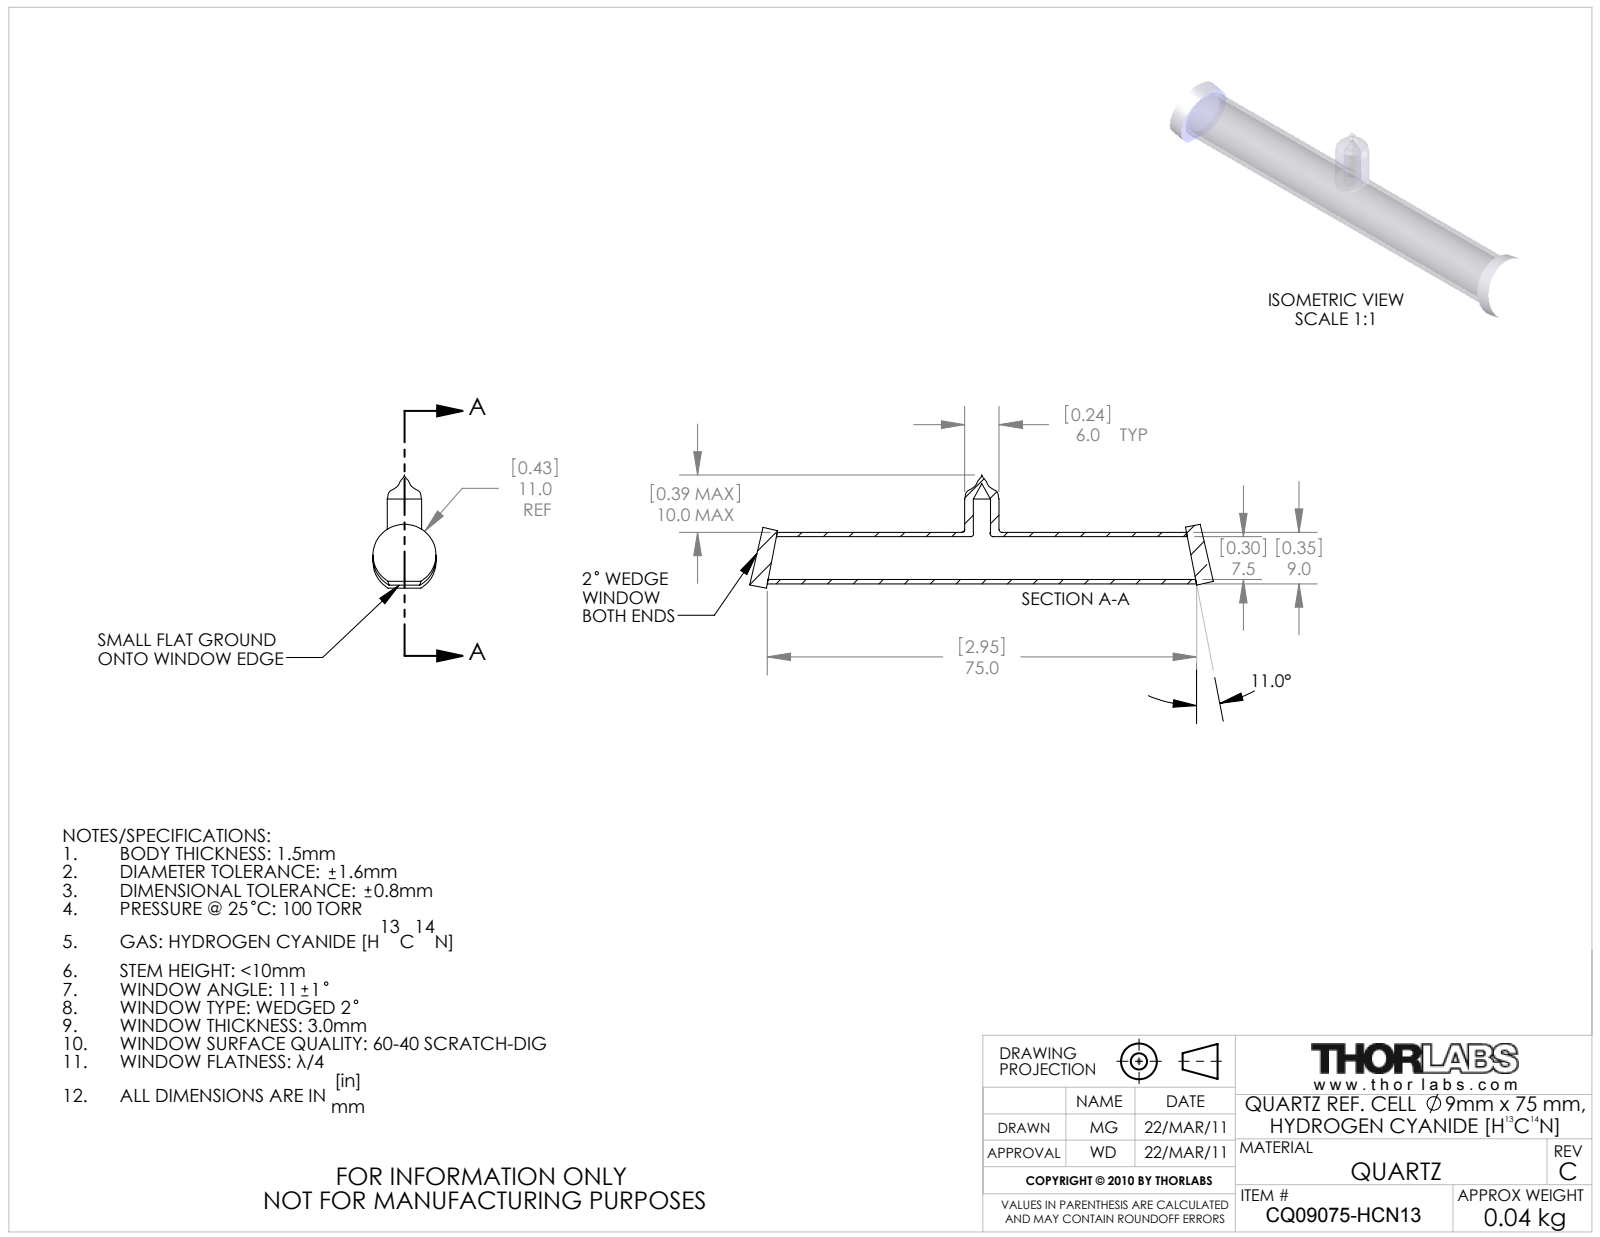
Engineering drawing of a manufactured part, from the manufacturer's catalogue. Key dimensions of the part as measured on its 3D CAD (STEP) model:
Part name (STEP PRODUCT): 12079-E0W
STEP written by: SolidWorks 2009 (AUTOMOTIVE_DESIGN)
Units: millimetres
Bodies: 3 solids, 33 faces (8 planar, 17 cylindrical, 8 other)
Overall size (bounding box): 55.95 × 19.74 × 11
Volume: 1 620 mm³ · Surface area: 3 311 mm²
Round holes (diameter × count): ⌀2.91 ×1, ⌀3 ×1, ⌀7.5 ×1
Round bosses / shafts (diameter × count): ⌀11 ×2, ⌀9 ×1, ⌀6 ×1
